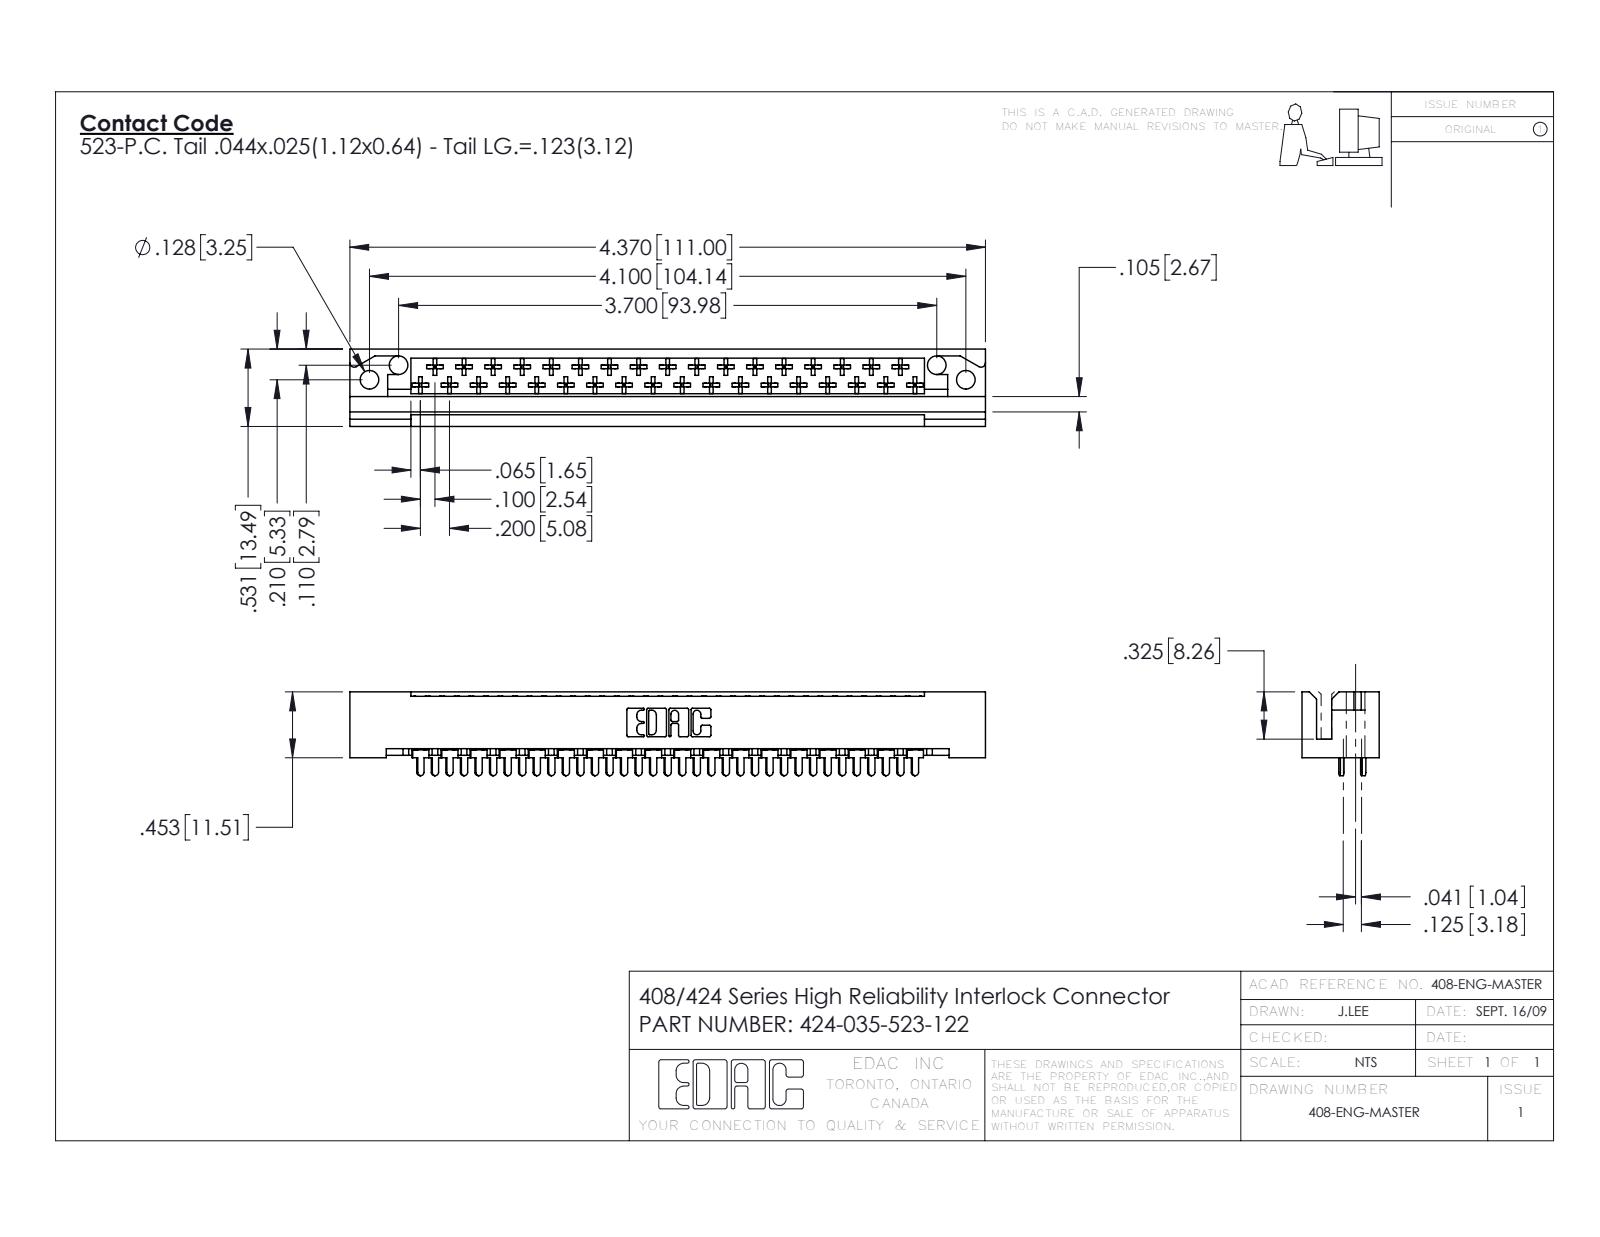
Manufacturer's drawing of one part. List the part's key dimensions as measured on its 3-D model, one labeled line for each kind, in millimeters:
Part name (STEP PRODUCT): 424-035-523-122; 424 Part_035; 408-290-001_408-290-123 - Top; 408-290-001_408-290-123 - Bottom
STEP written by: SolidWorks 2016 (CONFIG_CONTROL_DESIGN)
Units: millimetres
Bodies: 36 solids, 2070 faces (1559 planar, 371 cylindrical, 140 other)
Overall size (bounding box): 111 × 14.6 × 13.5
Volume: 11 500 mm³ · Surface area: 14 920 mm²
Round holes (diameter × count): ⌀3.3 ×4
Partial cylindrical surfaces — rounded edges, fillets, slot ends (radius × count): R0.3 ×210, R0.5 ×37, R0.6 ×35, R0.3 ×22, R0.2 ×6, R0.8 ×6, R0.7 ×3, R0.8 ×2
Main face-to-face distances: 2.5, 7.5, 0.6, 13.5, 3.2, 5.5, 6.9, 6, 6.6, 0.6
Hole centre spacings: 5.7, 99.1, 94, 104.1
